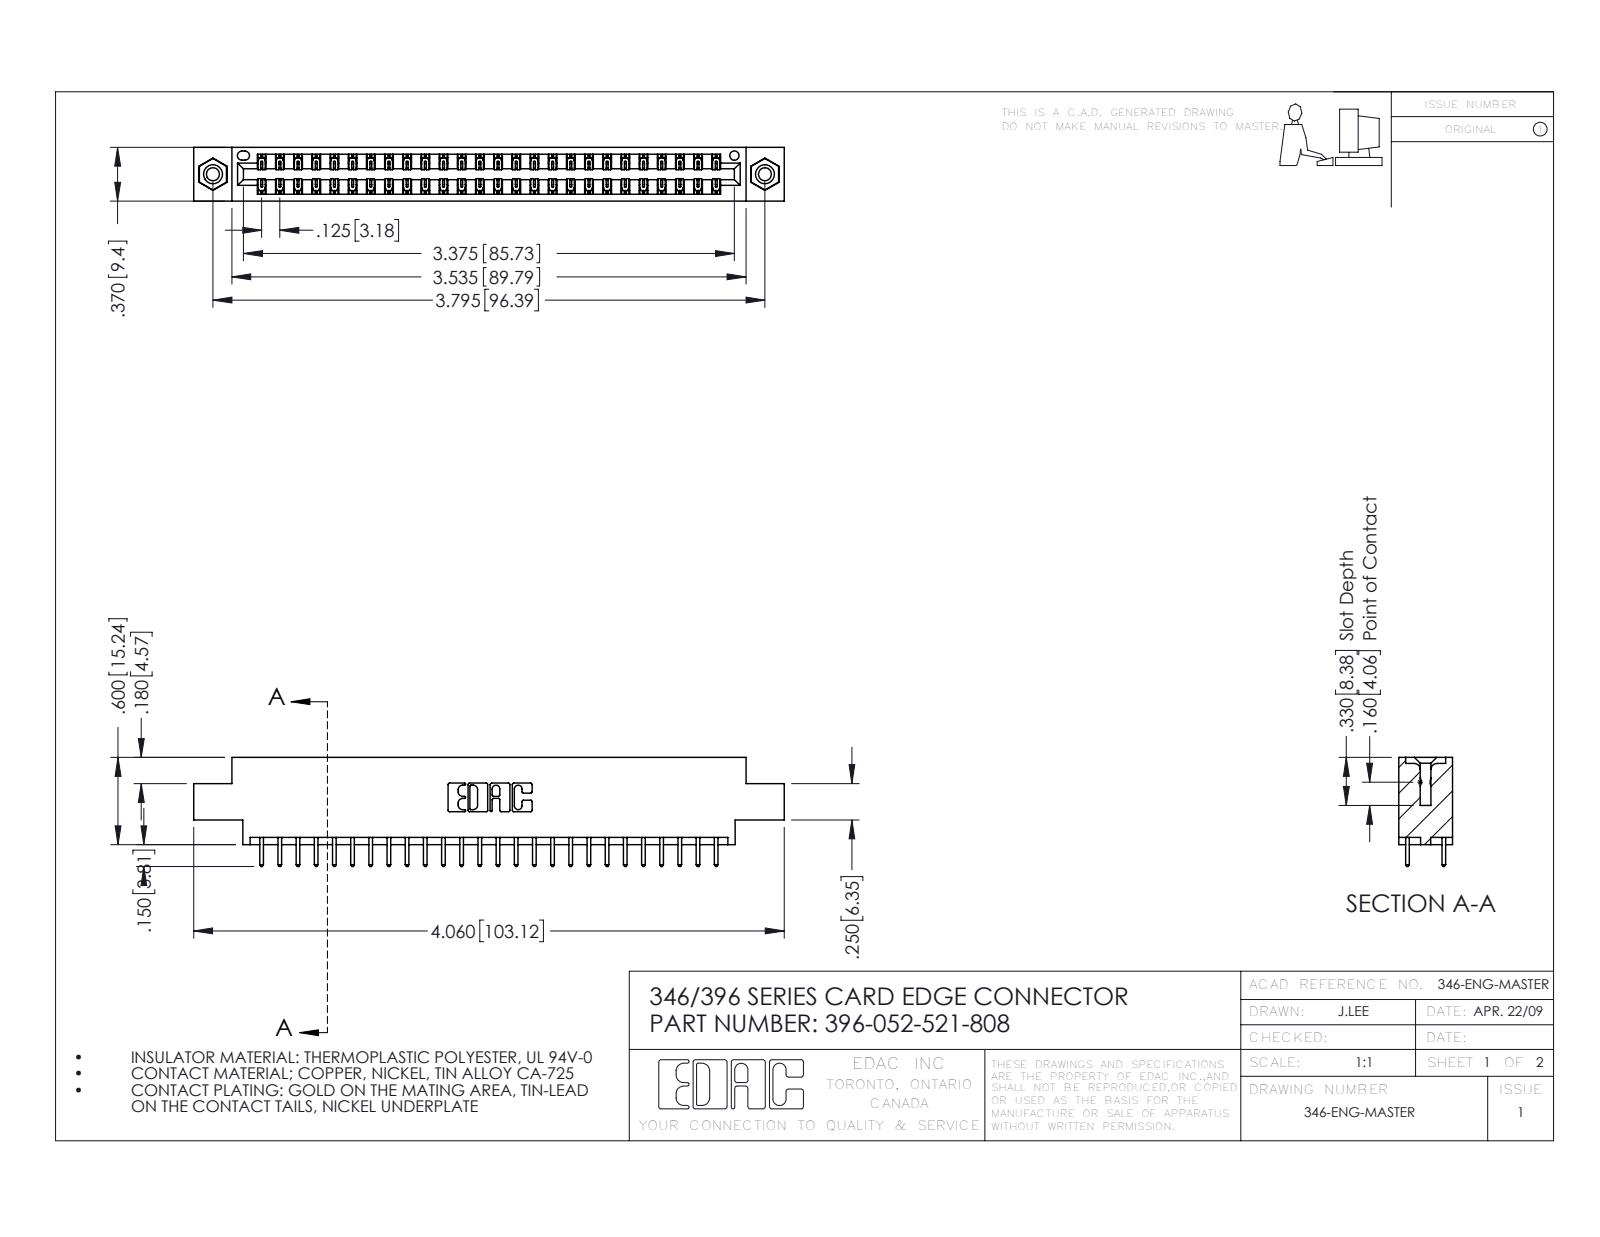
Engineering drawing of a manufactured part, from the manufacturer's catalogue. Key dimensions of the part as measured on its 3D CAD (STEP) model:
Part name (STEP PRODUCT): 345-250-001_345-250-003-102; 345-292-001_345-293-121; 396-052-521-808; 346 Part_0.170 Offset - 0.156 Dia-TI
STEP written by: SolidWorks 2016 (CONFIG_CONTROL_DESIGN)
Units: inches
Bodies: 55 solids, 2890 faces (1932 planar, 942 cylindrical, 16 other)
Overall size (bounding box): 4.06 × 0.75 × 0.37
Volume: 0.595 in³ · Surface area: 20.47 in²
Round holes (diameter × count): ⌀0.089 ×2, ⌀0.125 ×2, ⌀0.156 ×2, ⌀0.064 ×1
Round bosses / shafts (diameter × count): ⌀0.155 ×2
Partial cylindrical surfaces — rounded edges, fillets, slot ends (radius × count): R0.006 ×78, R0.01 ×52, R0.01 ×22, R0.007 ×6, R0.031 ×6, R0.026 ×3, R0.014 ×2, R0.022 ×2
Main face-to-face distances: 0.048, 0.322, 0.37, 0.25, 0.072, 0.298, 0.025, 0.275, 0.222, 0.148
Hole centre spacings: 0.246, 3.587, 3.795
